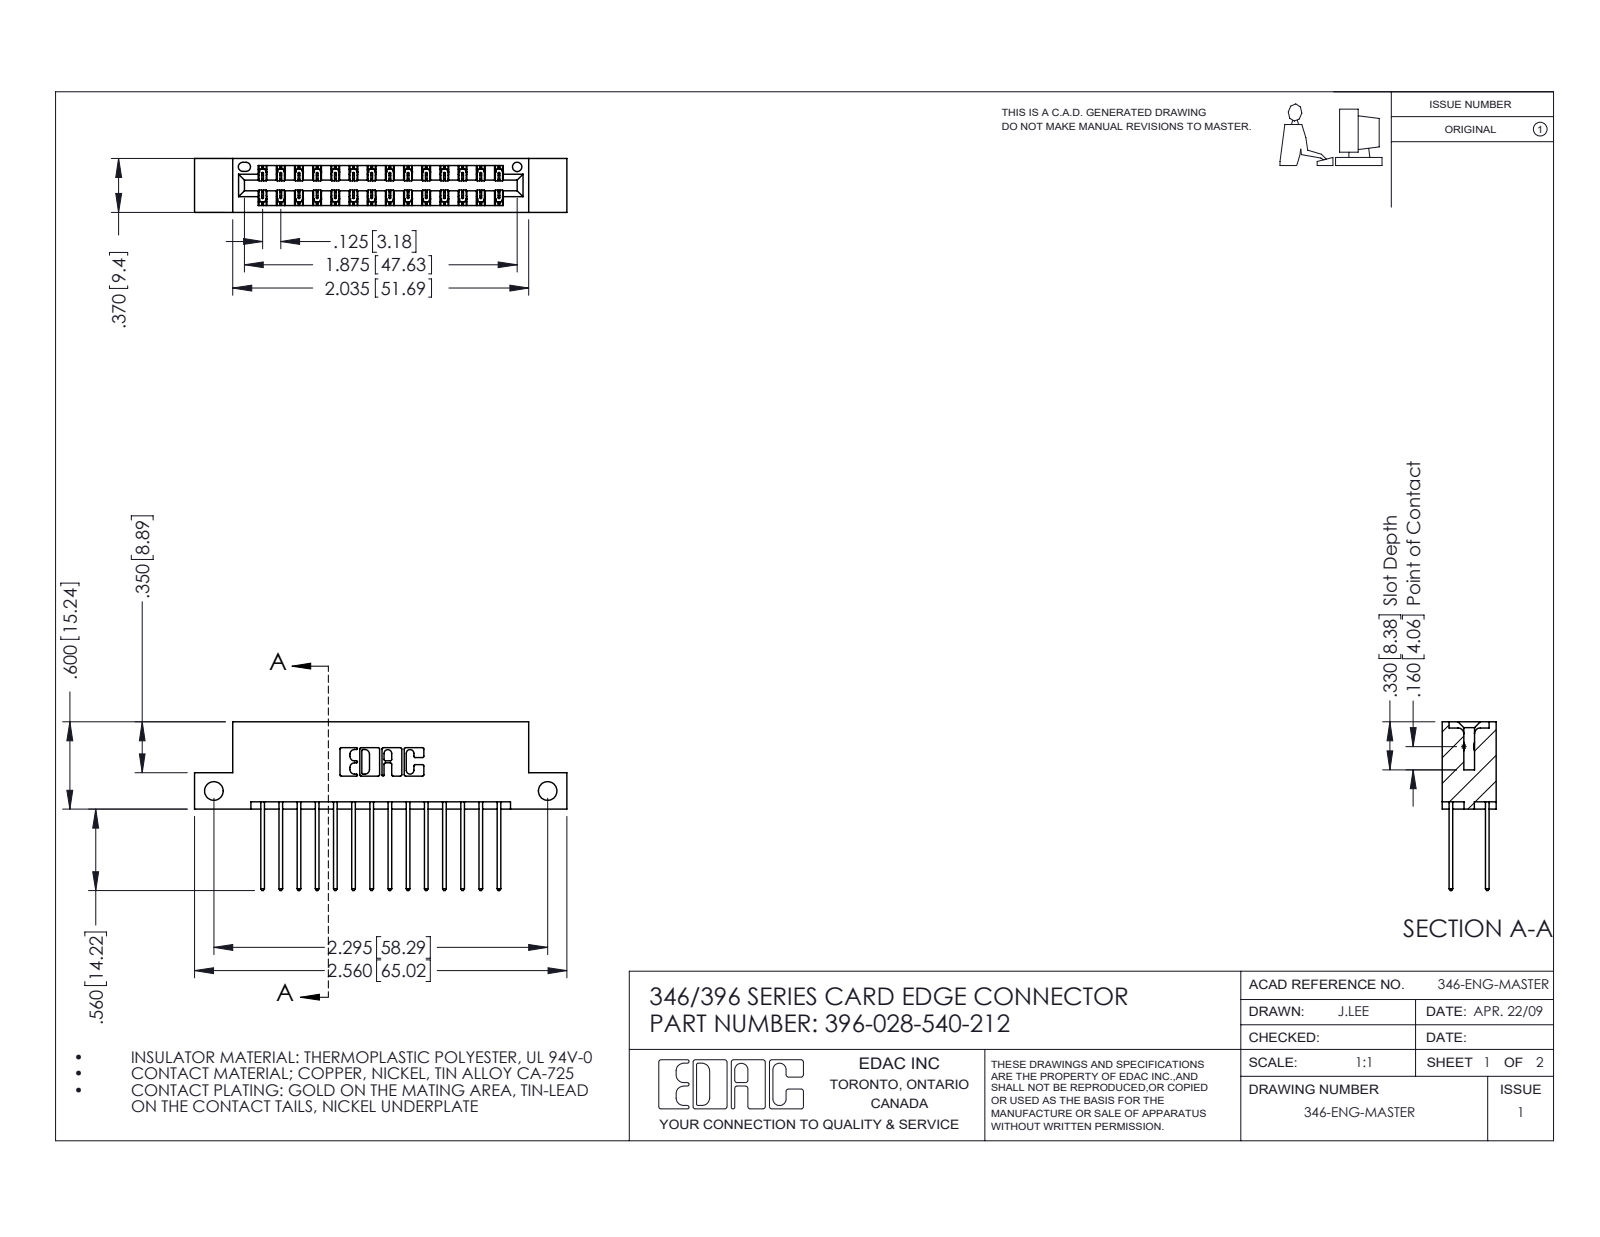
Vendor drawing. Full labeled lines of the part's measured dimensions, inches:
Part name (STEP PRODUCT): 396-028-540-212; 346 Part_Flush Mounting Lugs - Side Mount; 345-292-001_345-293-140
STEP written by: SolidWorks 2016 (CONFIG_CONTROL_DESIGN)
Units: inches
Bodies: 29 solids, 1578 faces (1056 planar, 522 cylindrical, 0 other)
Overall size (bounding box): 2.56 × 1.16 × 0.37
Volume: 0.375 in³ · Surface area: 12.97 in²
Round holes (diameter × count): ⌀0.128 ×2, ⌀0.064 ×1
Partial cylindrical surfaces — rounded edges, fillets, slot ends (radius × count): R0.006 ×42, R0.01 ×28, R0.01 ×22, R0.007 ×6, R0.031 ×6, R0.026 ×3, R0.014 ×2, R0.022 ×2
Main face-to-face distances: 0.25, 0.048, 0.322, 0.37, 0.072, 0.298, 0.025, 0.275, 0.148, 0.222
Hole centre spacings: 2.295
